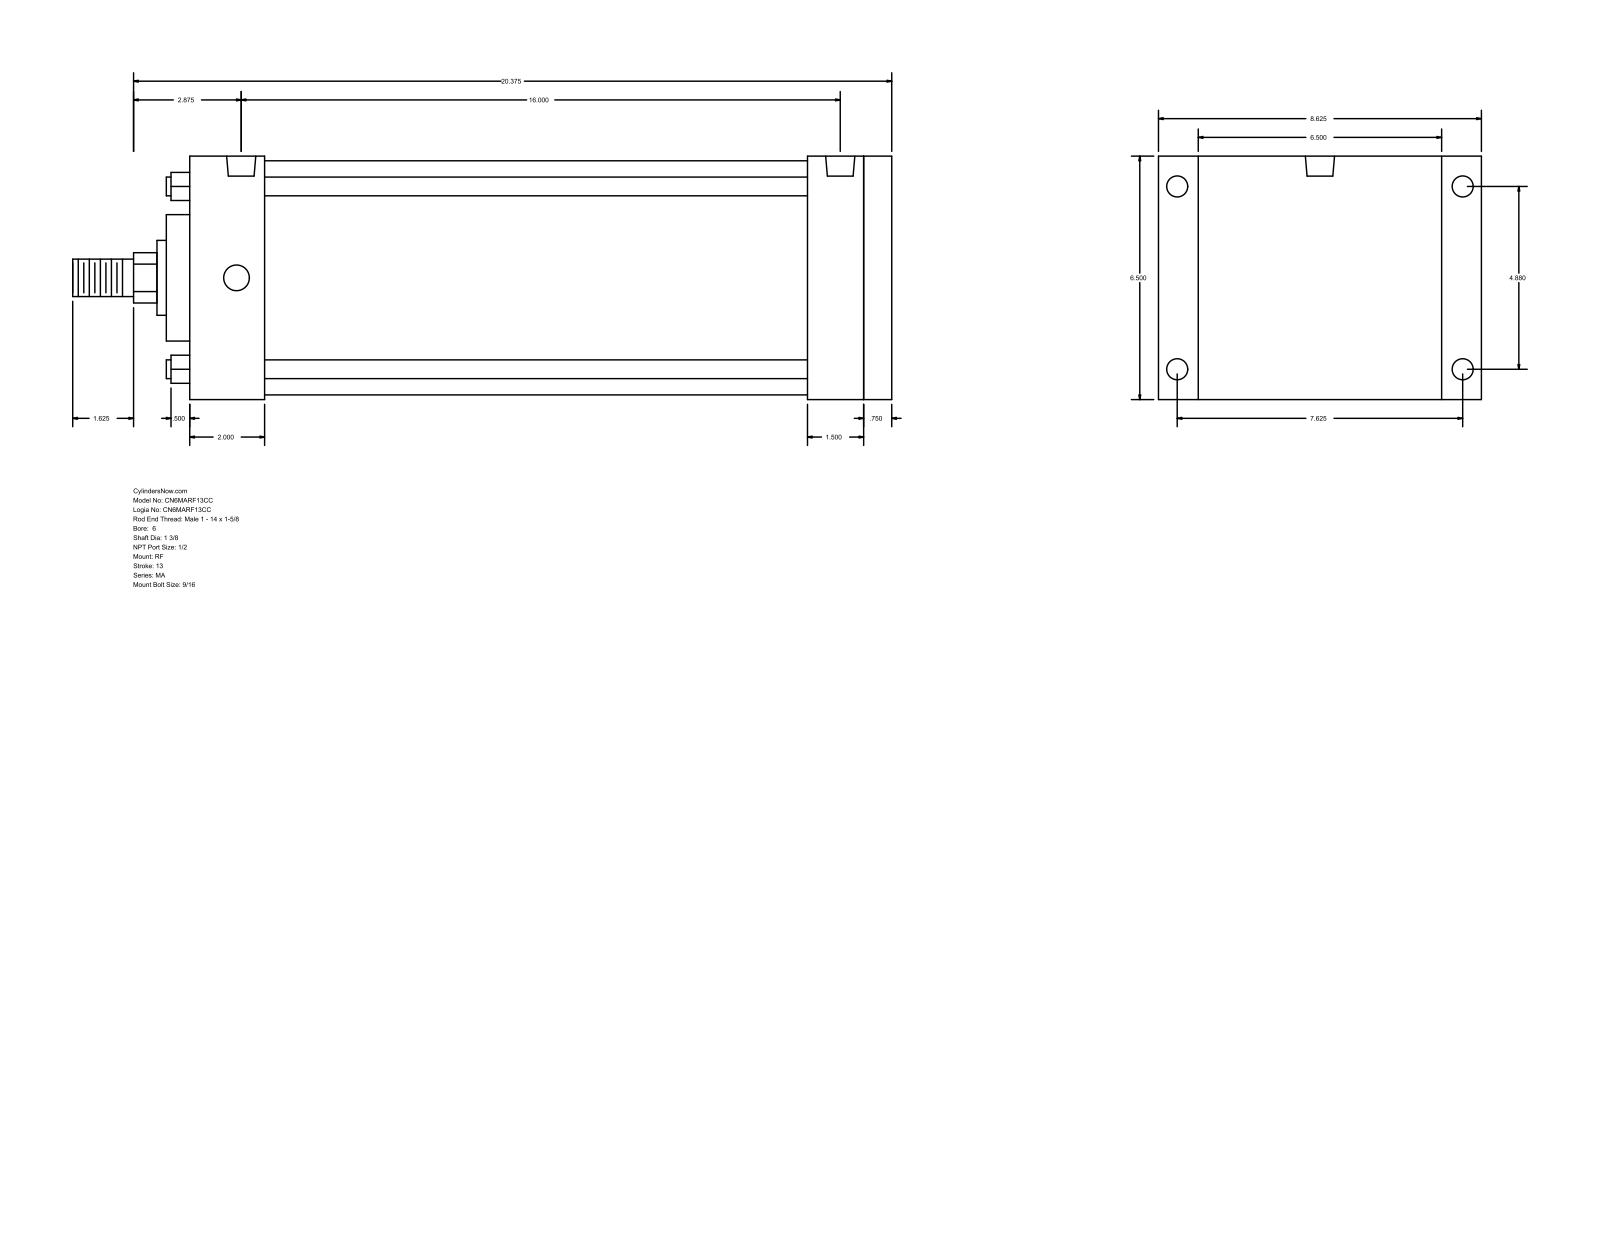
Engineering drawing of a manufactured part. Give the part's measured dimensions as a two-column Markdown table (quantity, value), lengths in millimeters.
| quantity | value |
| --- | --- |
| part name | MA_RF__0600_1.375 |
| STEP written by | GSSL Pune (CONFIG_CONTROL_DESIGN) |
| units | millimeters |
| bodies | 0 solids, 94 faces (65 planar, 29 cylindrical, 0 other) |
| overall size | 558.8 × 219.07 × 165.1 |
| round holes (diameter × count) | 14.29 × 4, 17.46 × 4, 19.77 × 2 |
| round bosses / shafts (diameter × count) | 12.7 × 4, 158.75 × 1, 85.72 × 1, 50.8 × 1, 34.92 × 1, 25.4 × 1 |
| partial cylindrical surfaces (radius × count) | 17.06 × 1 |
| main face-to-face distances | 165.1, 479.42, 460.38, 19.04, 38.1, 50.8, 409.58, 428.62, 422.28, 371.48 |
| hole center spacings | 123.96, 193.68, 229.95, 409.58, 3.18, 406.4 |
